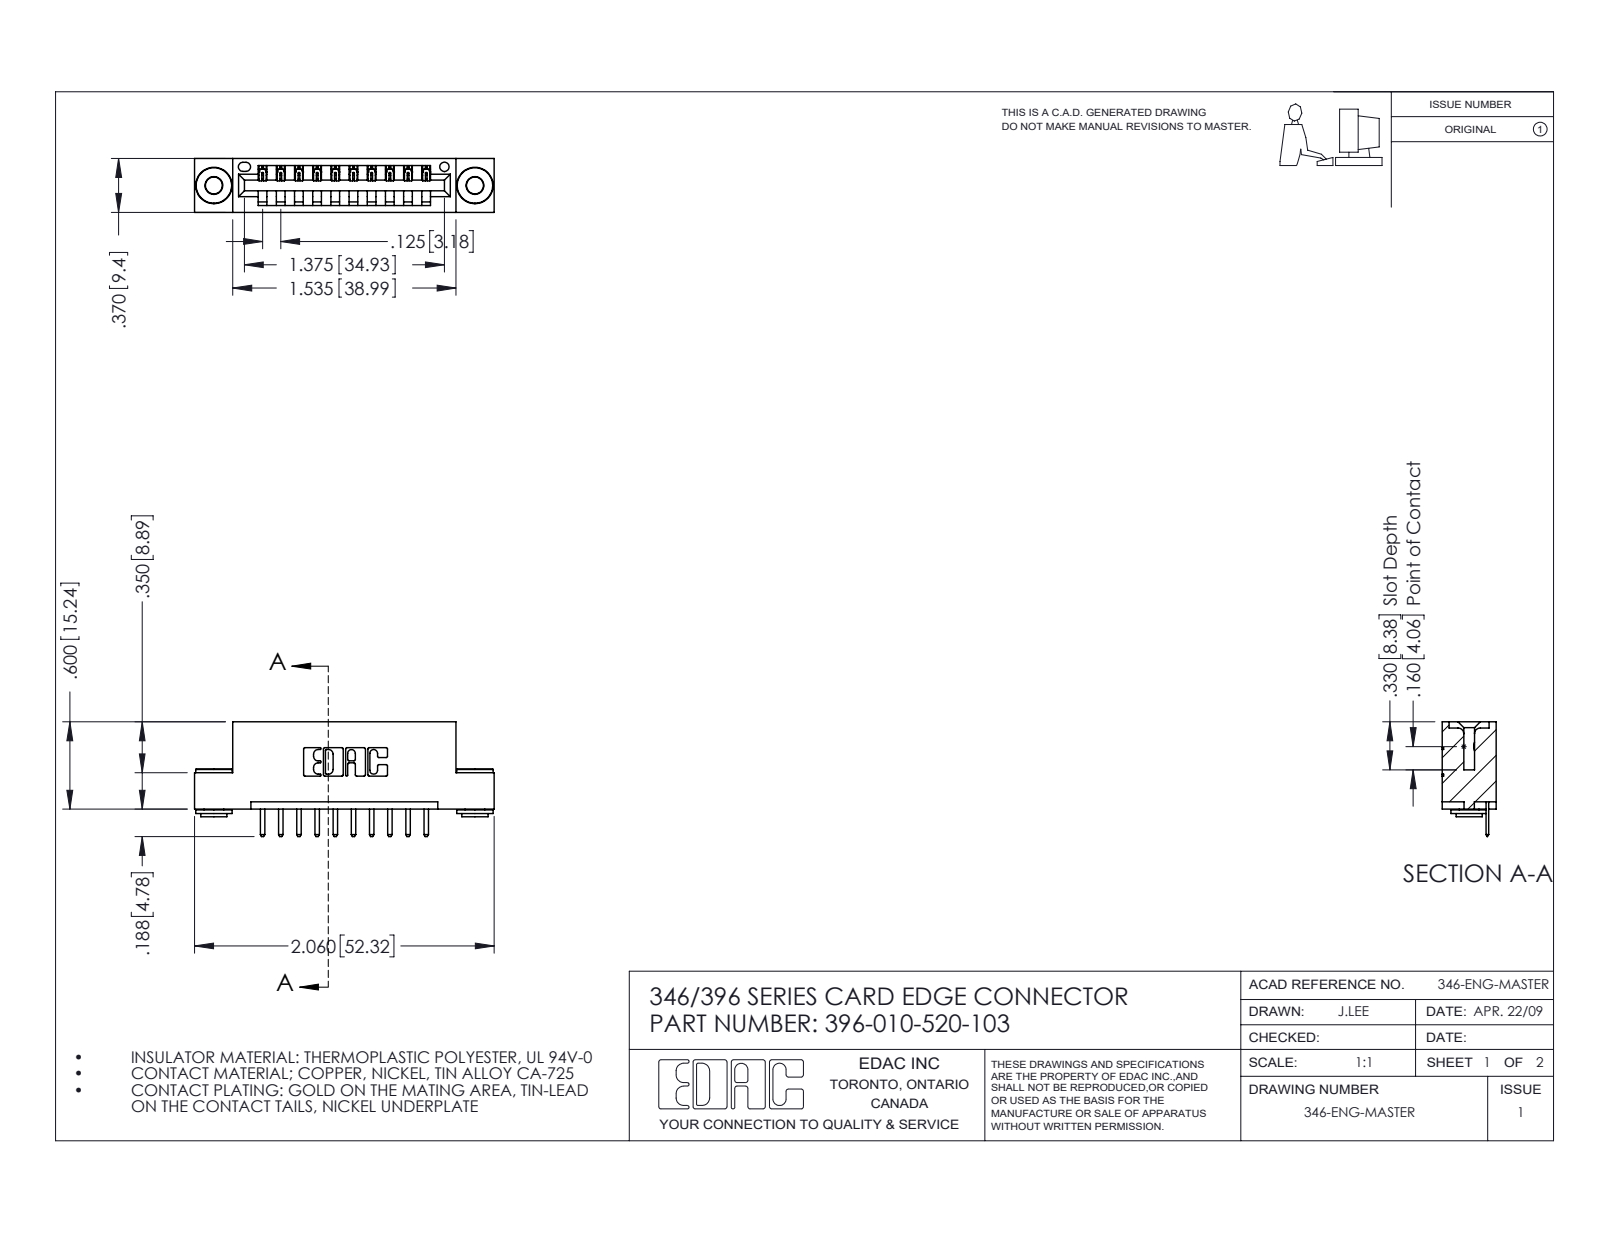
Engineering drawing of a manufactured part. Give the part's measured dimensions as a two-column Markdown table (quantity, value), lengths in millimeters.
| quantity | value |
| --- | --- |
| part name | 345-250-002_345-250-002-102; 396-010-520-103; 346 Part_Flush Mounting Lugs - 0.156 Dia-TH; 345-292-001_345-293-120 |
| STEP written by | SolidWorks 2016 (CONFIG_CONTROL_DESIGN) |
| units | millimeters |
| bodies | 13 solids, 780 faces (506 planar, 266 cylindrical, 8 other) |
| overall size | 52.3 × 20 × 9.4 |
| volume | 4 790 mm³ |
| surface area | 5 750 mm² |
| round holes (diameter × count) | 2.9 × 2, 4 × 2, 1.6 × 1 |
| round bosses / shafts (diameter × count) | 6.4 × 2, 4.6 × 2, 3.5 × 2 |
| partial cylindrical surfaces (radius × count) | 0.3 × 22, 0.3 × 22, 0.2 × 20, 0.2 × 6, 0.8 × 6, 0.7 × 3, 0.8 × 2, 1 × 2 |
| main face-to-face distances | 6.4, 9.4, 1.2, 8.2, 3.8, 5.6, 2.5, 4.4, 0.6, 1.8 |
| hole center spacings | 6.2, 40.4, 45.6 |
